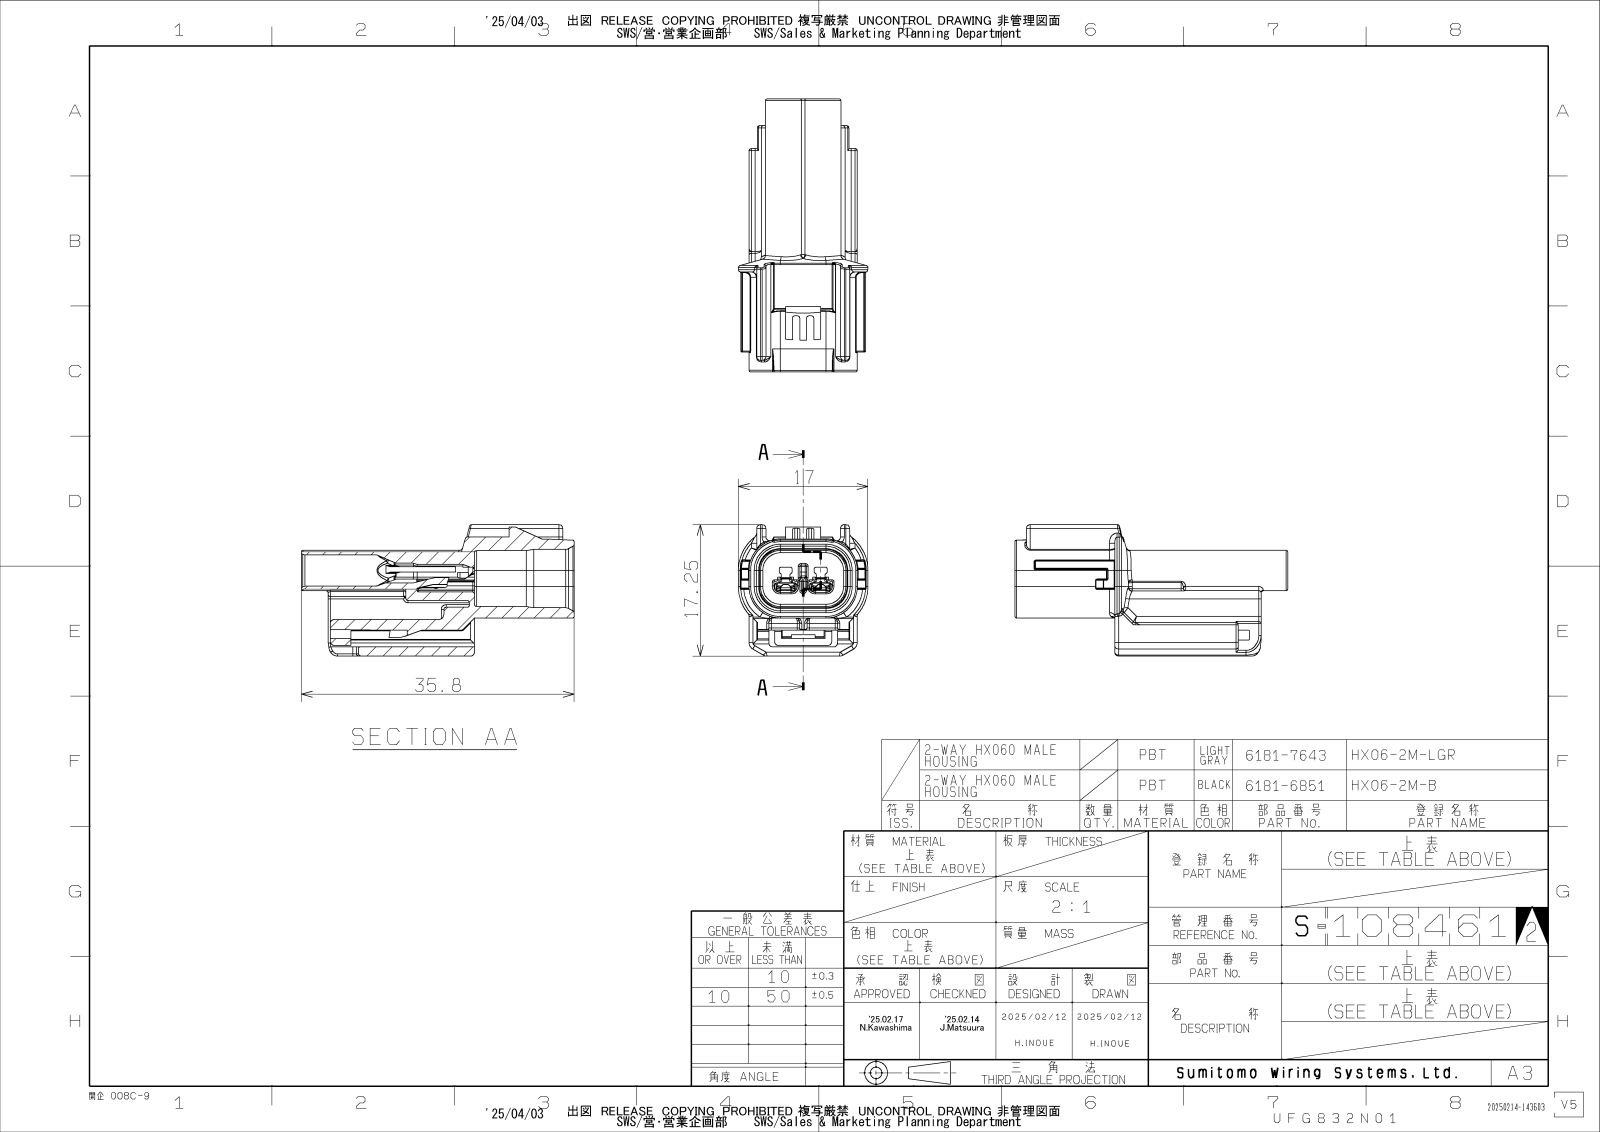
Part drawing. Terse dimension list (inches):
name: 6181-6851
written by: CATIA V5 STEP AP214 v2 (AUTOMOTIVE_DESIGN)
unit: in
bodies: 1 solid, 210 faces (150 planar, 39 cylindrical, 21 other)
size: 1.409 × 0.679 × 0.669
volume: 0.181 in³; area: 5.847 in²
holes: 2× ⌀0.161
bosses: 2× ⌀0.209
rounds: 4× R0.039, 4× R0.043, 4× R0.102, 4× R0.108, 4× R0.161, 4× R0.217, 2× R0.079, 2× R0.199
face distances: 0.039, 0.457, 0.063, 0.047, 0.087, 0.024, 0.134, 0.354, 0.102, 0.142
hole spacings: 0.181
